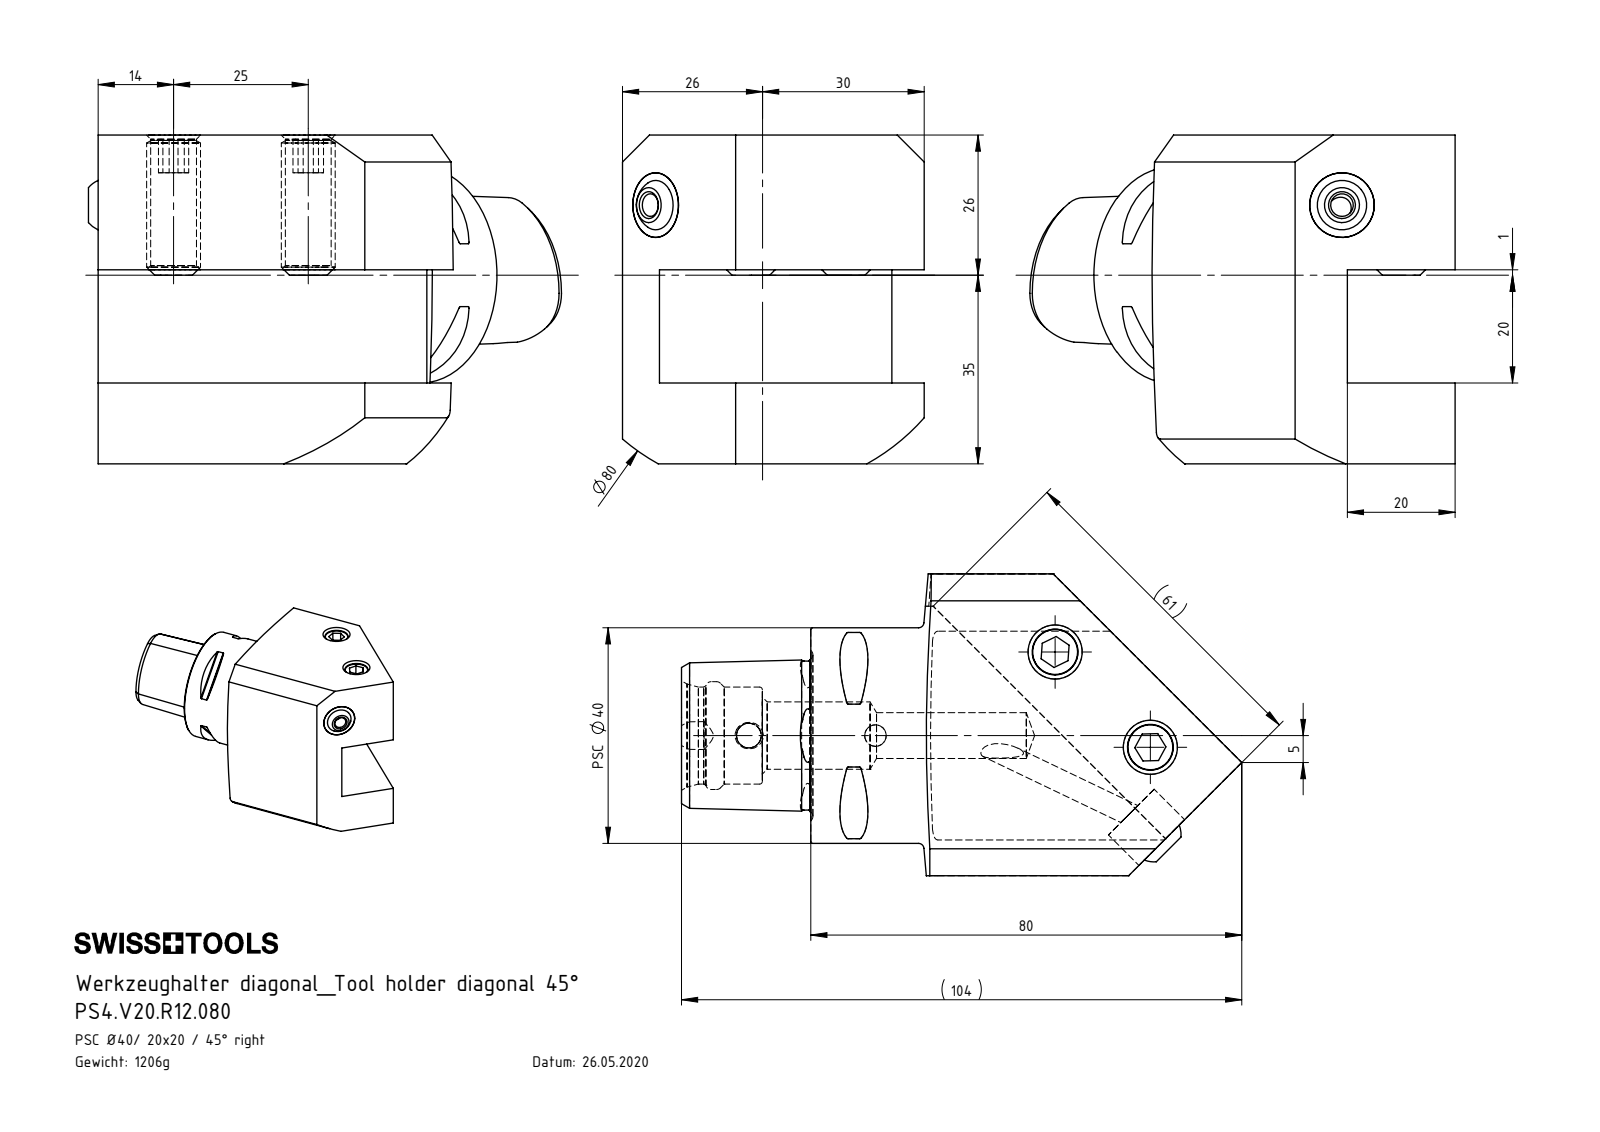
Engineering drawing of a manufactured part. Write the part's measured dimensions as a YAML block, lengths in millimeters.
part_name: "PS4.V20.R12.080; ISO 4026 - M10 x 25; KU1-U12.001.010_1; PS4-V20.R12.080_A (+2 more)"
step_written_by: "SolidWorks 2017 (AUTOMOTIVE_DESIGN)"
units: millimeters
bodies: {solids: 5, faces: 153, planar: 54, cylindrical: 29, other: 70}
overall_size: [104, 61, 56]
volume: 153962
surface_area: 29612
round_holes:
  - {diameter: 8.5, count: 3}
  - {diameter: 4.2, count: 2}
  - {diameter: 4, count: 1}
  - {diameter: 4.6, count: 1}
  - {diameter: 7, count: 1}
  - {diameter: 12, count: 1}
  - {diameter: 12.5, count: 1}
  - {diameter: 18, count: 1}
  - {diameter: 20, count: 1}
round_bosses_or_shafts:
  - {diameter: 10, count: 2}
  - {diameter: 40, count: 1}
partial_cylinders:
  - {radius: 0.3, count: 8}
  - {radius: 3, count: 1}
  - {radius: 40, count: 1}
face_to_face_distances: [61, 20, 15, 46, 25, 36, 21, 56, 24, 8]
hole_center_spacings: [23.5, 25, 36.78, 51.08, 58.93, 74.56]
